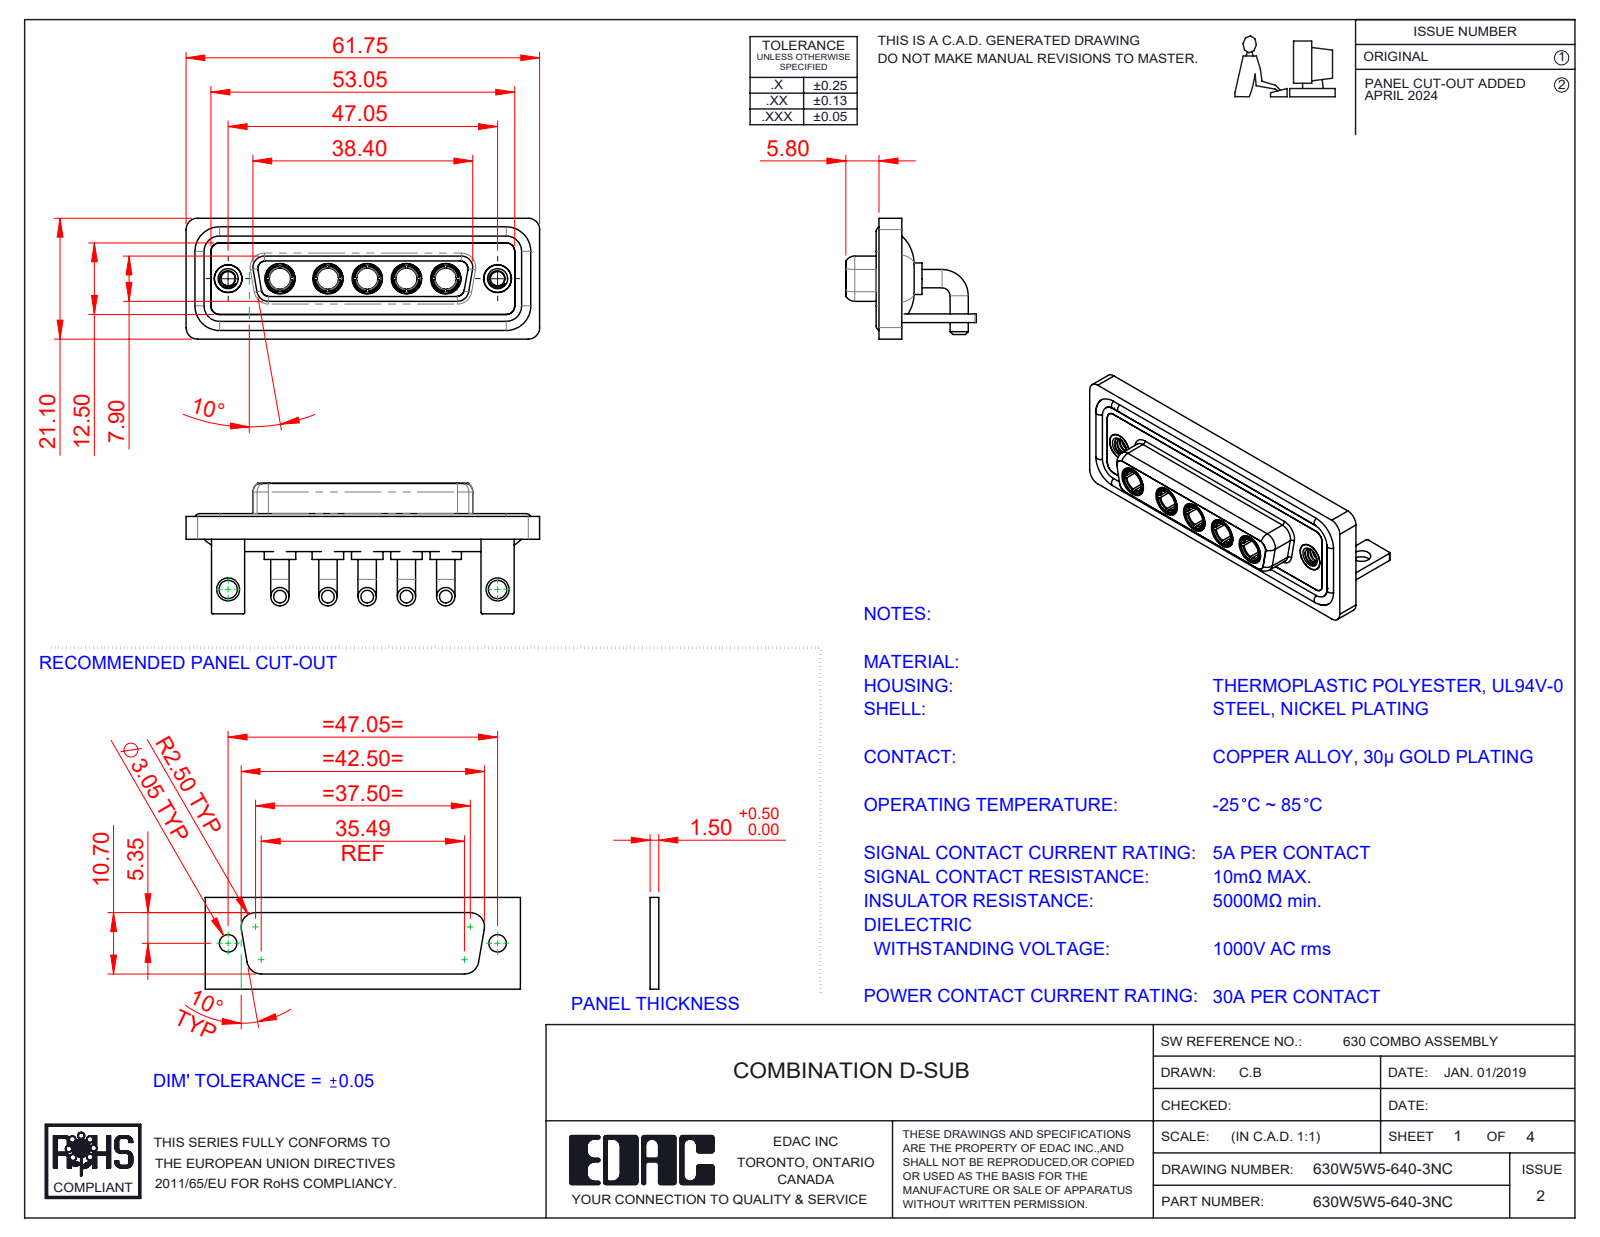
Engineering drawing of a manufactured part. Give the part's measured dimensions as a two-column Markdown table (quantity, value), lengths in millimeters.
| quantity | value |
| --- | --- |
| part name | 630Combo Threaded Rivet_A; 630Combo Housing_5W5; Power Socket_30A RA; 630Combo Stabilizer Bracket_50 Contacts (+4 more) |
| STEP written by | SolidWorks 2023 (CONFIG_CONTROL_DESIGN) |
| units | millimeters |
| bodies | 19 solids, 818 faces (270 planar, 335 cylindrical, 213 other) |
| overall size | 61.75 × 22.8 × 21.1 |
| volume | 8 934 mm³ |
| surface area | 14 644 mm² |
| round holes (diameter × count) | 4.85 × 7, 3.7 × 5, 5.3 × 5, 2.5 × 2, 3.2 × 2, 4 × 2, 4.05 × 2, 5 × 2 |
| round bosses / shafts (diameter × count) | 3.2 × 10, 5.5 × 5, 5.2 × 5, 4.96 × 5, 4.75 × 5, 3.75 × 5, 1.6 × 4, 4.95 × 2 |
| partial cylindrical surfaces (radius × count) | 2 × 19, 1.5 × 18, 0.25 × 16, 1.35 × 8, 1.6 × 8, 0.5 × 5, 2.1 × 5, 0.6 × 4 |
| main face-to-face distances | 0.4, 1.8, 2.9, 3.7, 1.5, 4.1, 1.1, 1.4, 1.6, 2.5 |
| hole center spacings | 6.86, 9.04, 38.01, 47.05, 6.87, 8.38, 13.72, 13.73 |
